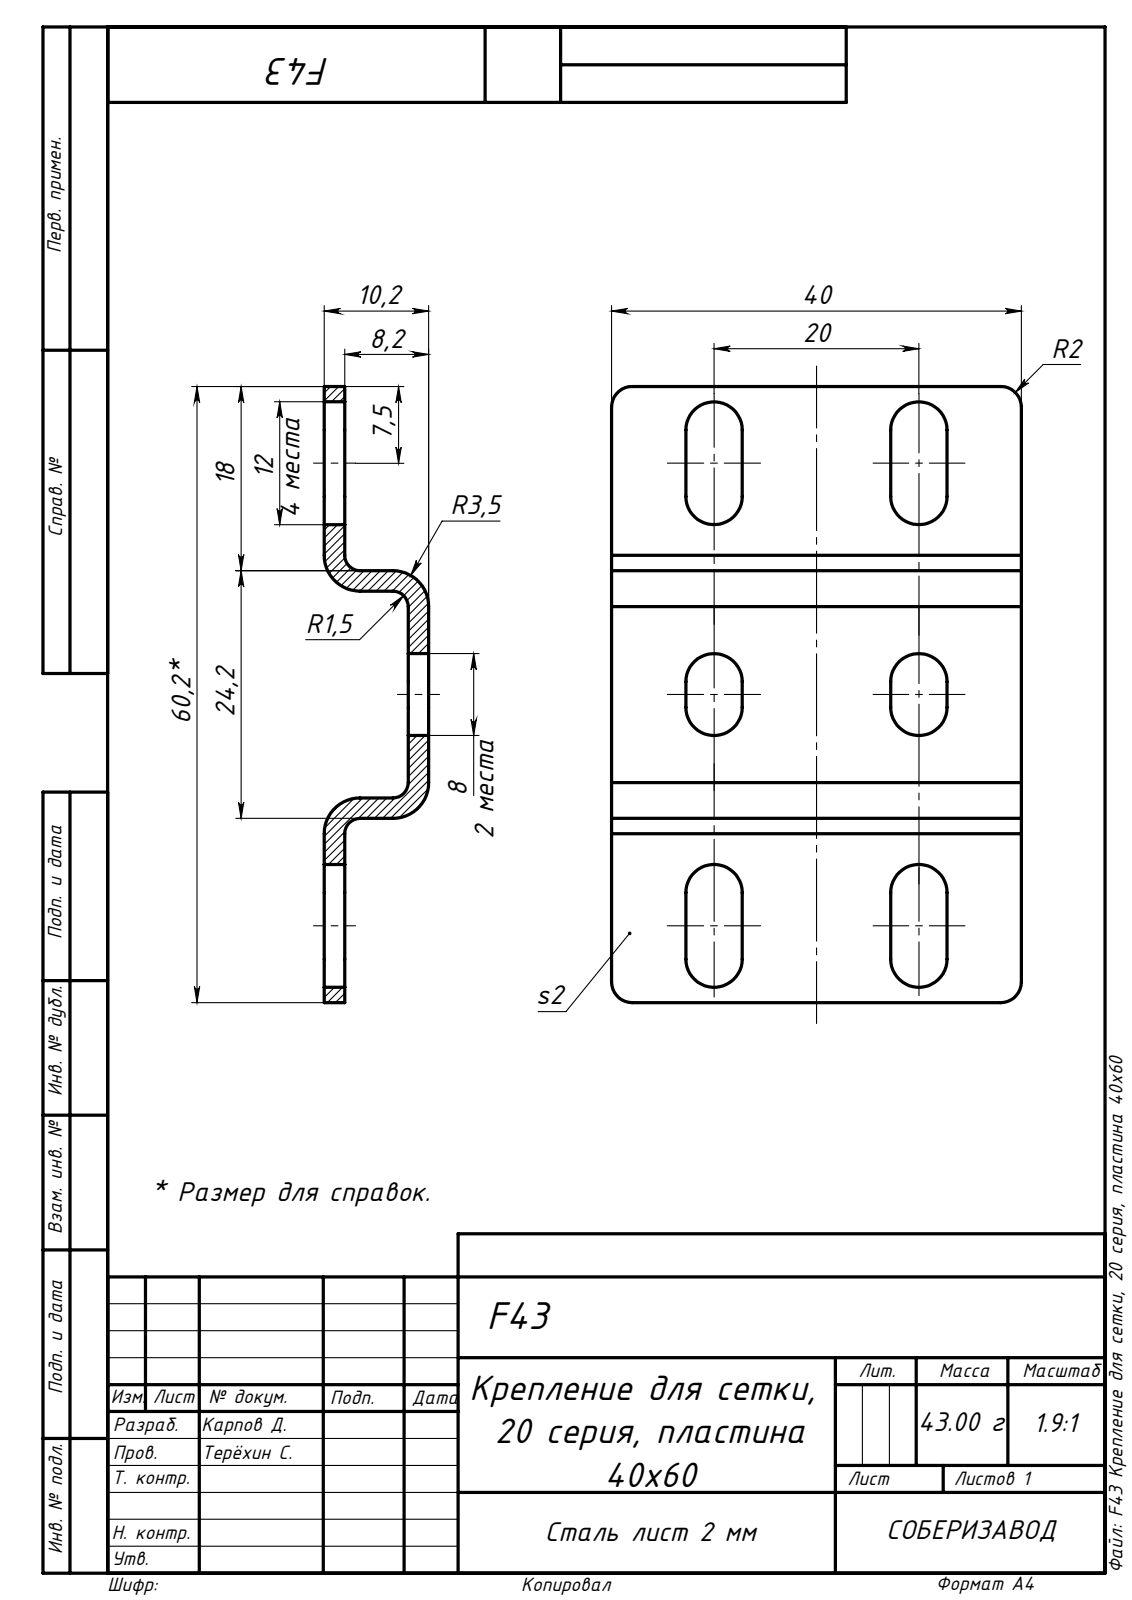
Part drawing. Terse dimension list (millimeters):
name: F43 Крепление для сетки, 20 серия, пластина 40х60
written by: SolidWorks 2019 (AUTOMOTIVE_DESIGN)
unit: mm
bodies: 1 solid, 70 faces (42 planar, 28 cylindrical, 0 other)
size: 60.2 × 40 × 10.2
volume: 5 152 mm³; area: 5 925 mm²
rounds: 12× R2.75, 4× R1.5, 4× R2, 4× R3.5
face distances: 2, 8.2, 10.2, 6.2, 22.2, 20, 18, 40.2, 42.2, 40
